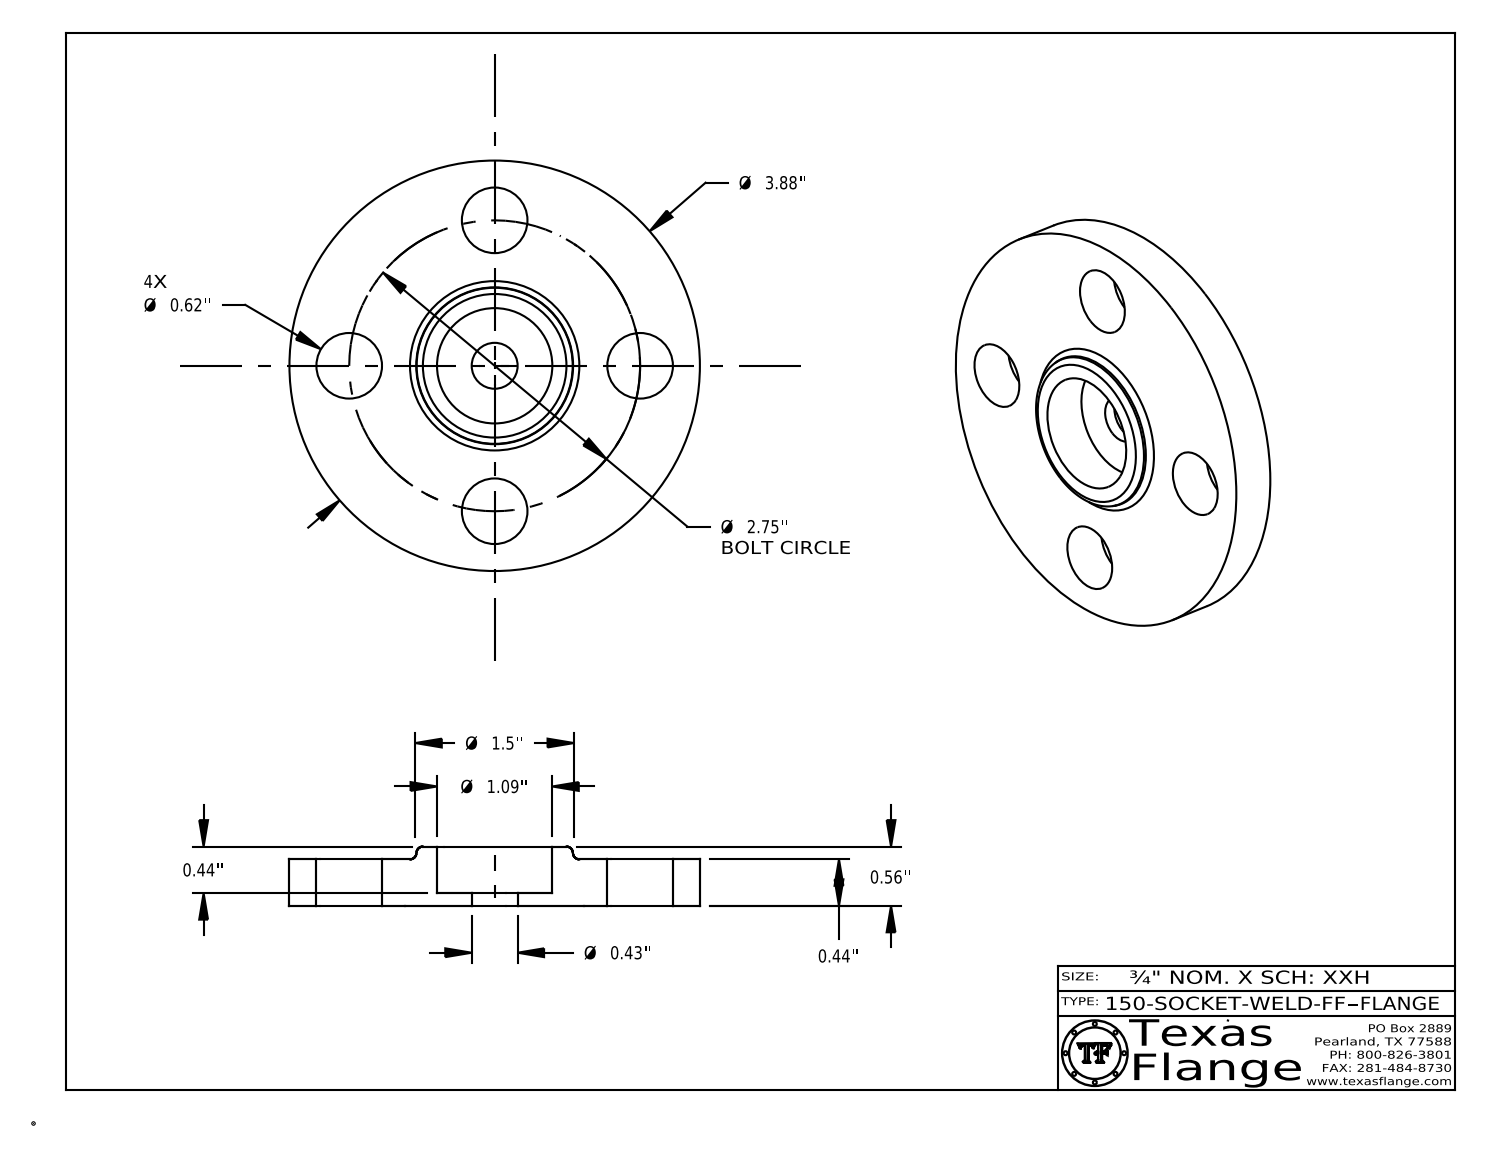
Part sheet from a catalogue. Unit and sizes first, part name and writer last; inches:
Units: inches
Overall size (bounding box): 3.88 × 3.88 × 0.56
Round holes (diameter × count): ⌀0.62 ×4, ⌀0.434 ×1, ⌀0.495 ×1, ⌀1.09 ×1
Round bosses / shafts (diameter × count): ⌀0.03 ×8, ⌀3.88 ×1, ⌀0.39 ×1
Main face-to-face distances: 0.44, 0.12, 0.32, 0.56, 0.44, 0.12, 0.425, 0.305, 0.015, 0.135
Hole centre spacings: 1.375, 1.945, 1.052, 2.541, 2.75
Volume: 4.448 in³ · Surface area: 31.8 in²
Bodies: 1 solid, 410 faces (370 planar, 34 cylindrical, 6 other)
Part name (STEP PRODUCT): 150-SOCKET-WELD-FF
STEP written by: CATIA V5 STEP AP214 (AUTOMOTIVE_DESIGN)
